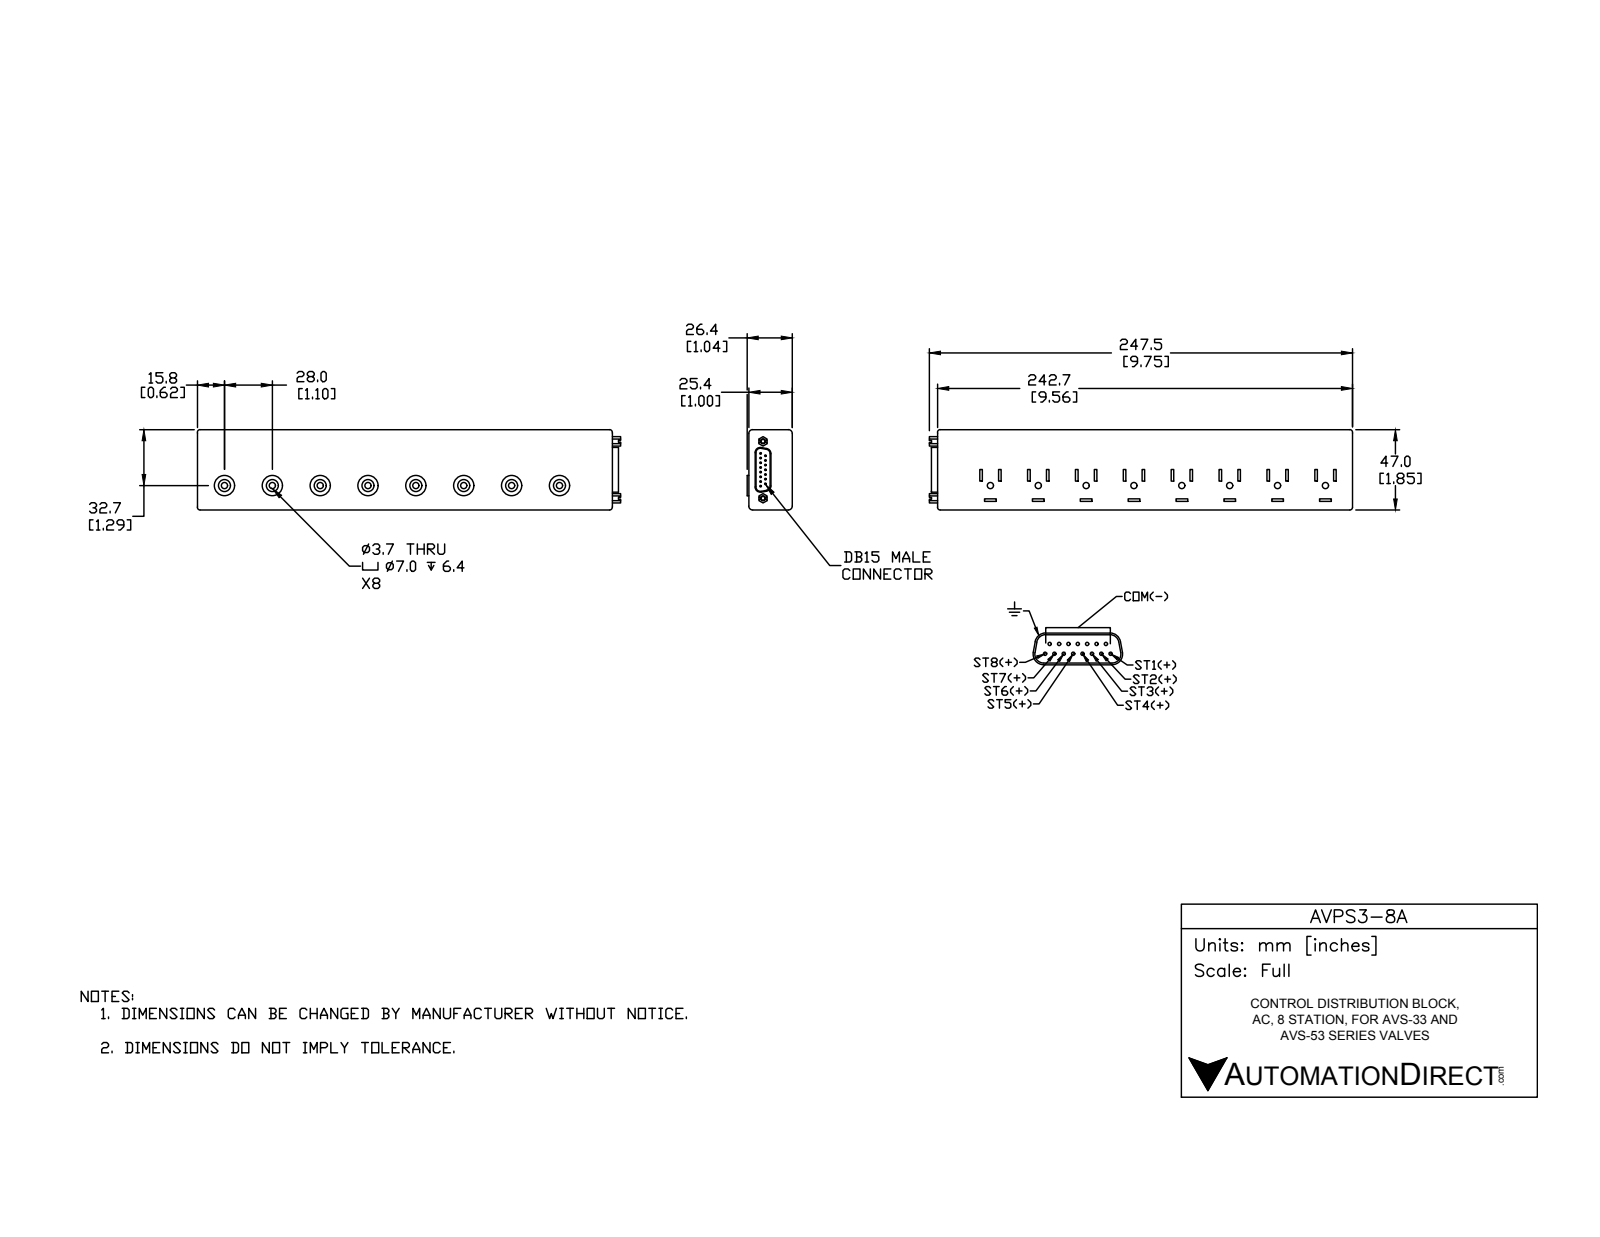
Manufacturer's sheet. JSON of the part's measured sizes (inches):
{"part_name": "AVPS3-8A", "step_written_by": "SolidWorks 2016 (AUTOMOTIVE_DESIGN)", "units": "inches", "bodies": {"solids": 1, "faces": 311, "planar": 195, "cylindrical": 104, "other": 12}, "overall_size": [9.743, 1.85, 1.04], "volume_in3": 17.32, "surface_area_in2": 66.88, "round_holes": [[0.145, 8], [0.275, 8], [0.089, 2]], "round_bosses_or_shafts": [[0.039, 15], [0.469, 8]], "partial_cylinders_radius": [[0.062, 8], [0.09, 4], [0.102, 4], [0.122, 4]], "face_to_face_distances": [1, 1.85, 9.554, 0.04, 1.04, 0.059, 1.102, 0.25, 0.79, 2.204], "hole_center_spacings": [1.102, 2.204, 4.408, 3.306, 5.51, 2.204, 3.306, 6.612]}
